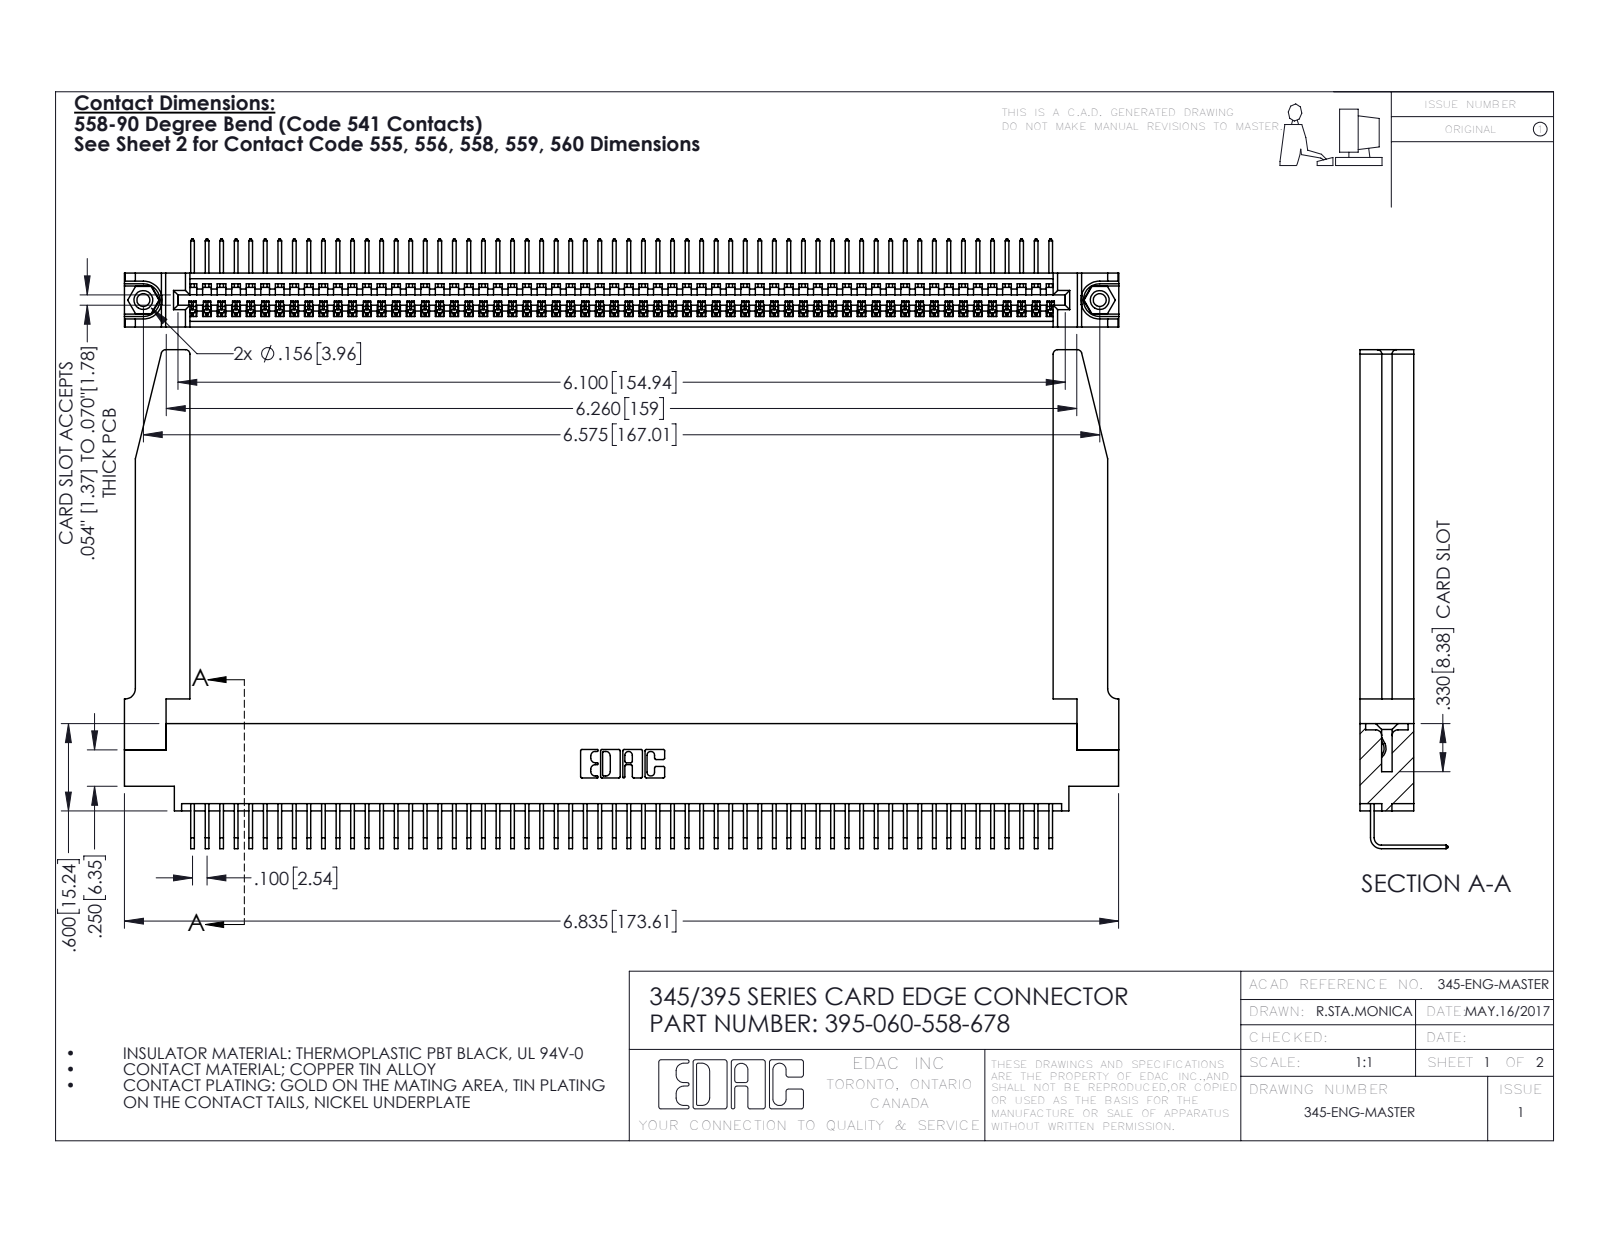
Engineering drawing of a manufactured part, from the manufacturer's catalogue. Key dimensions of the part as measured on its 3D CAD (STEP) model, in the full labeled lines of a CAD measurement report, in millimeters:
Part name (STEP PRODUCT): 345-250-001_345-250-001-102; 345-292-001_558 Tail - 2; 395-060-558-678; 345-220-078_345-220-078 (+1 more)
STEP written by: SolidWorks 2016 (CONFIG_CONTROL_DESIGN)
Units: millimetres
Bodies: 65 solids, 3964 faces (2746 planar, 1166 cylindrical, 52 other)
Overall size (bounding box): 173.6 × 87.1 × 15.4
Volume: 24 500 mm³ · Surface area: 30 620 mm²
Round holes (diameter × count): ⌀2.3 ×2, ⌀3.2 ×2, ⌀4 ×2, ⌀1.6 ×1
Round bosses / shafts (diameter × count): ⌀3.9 ×2
Partial cylindrical surfaces — rounded edges, fillets, slot ends (radius × count): R0.2 ×120, R0.3 ×22, R0.8 ×8, R0.2 ×6, R0.8 ×6, R0.7 ×3, R0.8 ×2, R1 ×2
Main face-to-face distances: 9.4, 1.8, 7.6, 2.5, 6.9, 0.6, 5.1, 5.7, 3.8, 3.8
Hole centre spacings: 6.9, 161, 167
